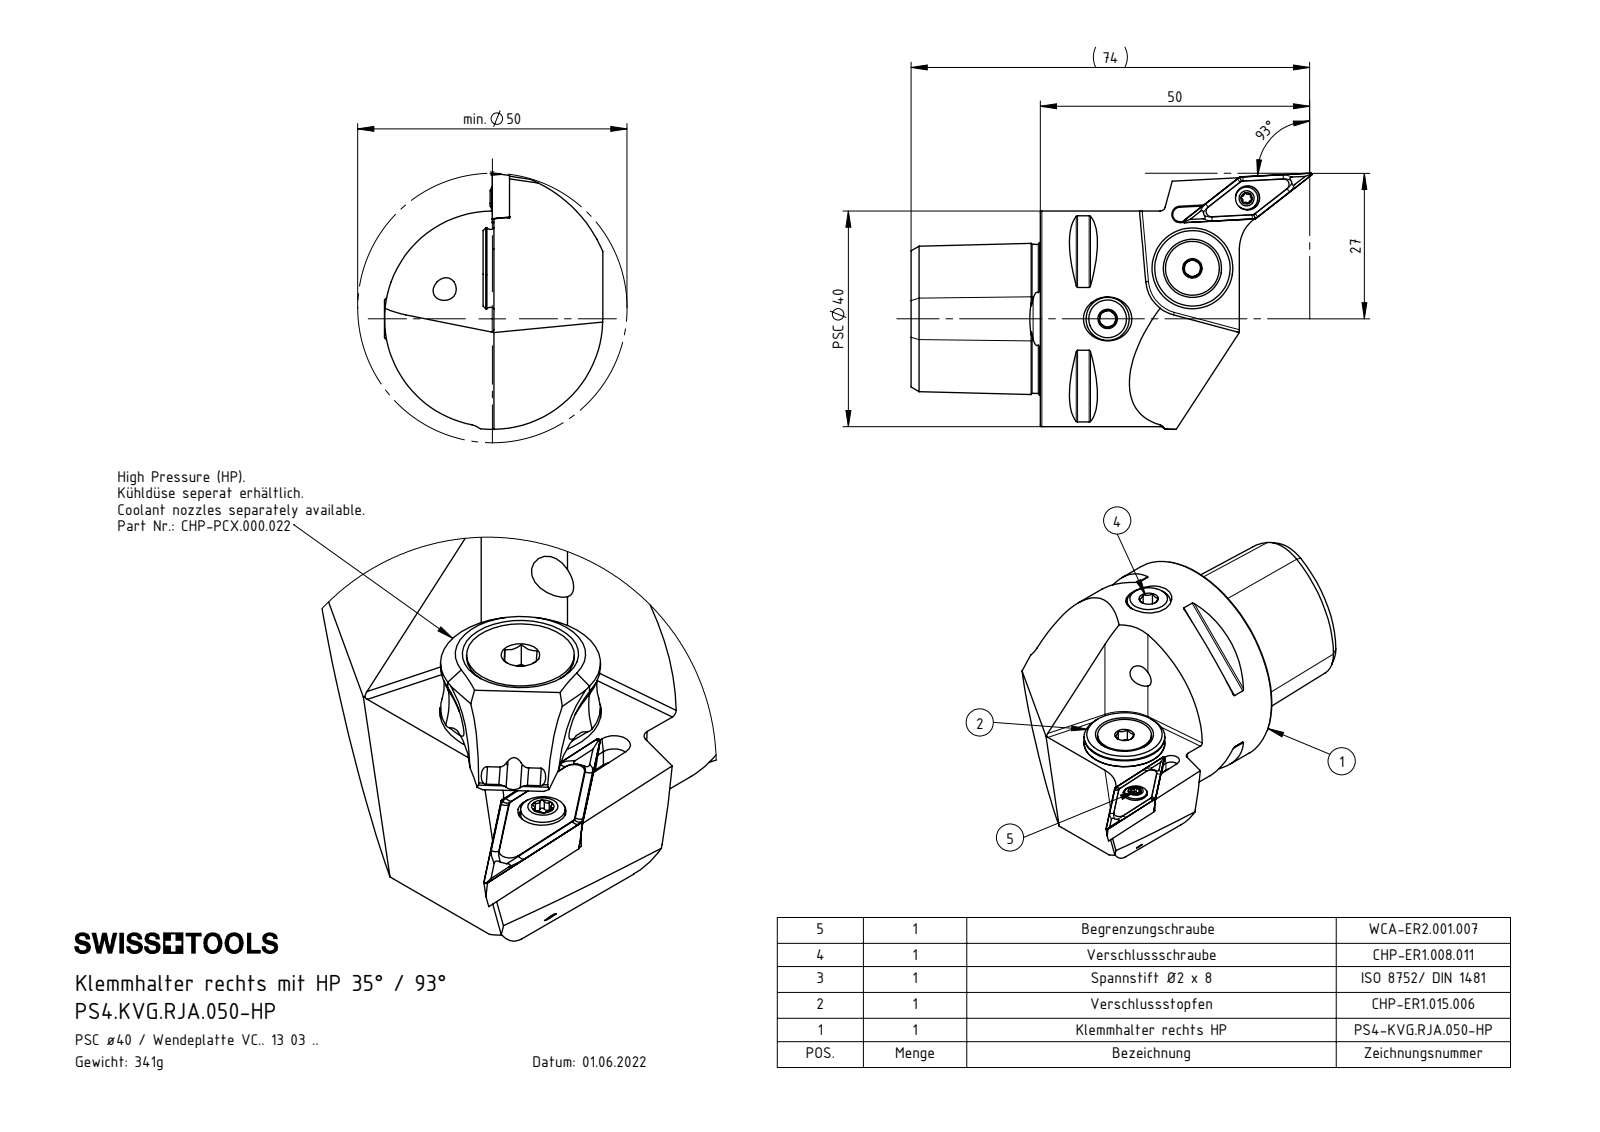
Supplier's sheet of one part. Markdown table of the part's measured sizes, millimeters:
| quantity | value |
| --- | --- |
| part name | CHP-PCX.000.022_Düse; PS4-KVG.RJA.050-HP_B; DIN 7991 - M5x18; CHP-ER1.008.011_A (+7 more) |
| STEP written by | SolidWorks 2022 (AUTOMOTIVE_DESIGN) |
| units | millimeters |
| bodies | 9 solids, 491 faces (107 planar, 134 cylindrical, 250 other) |
| overall size | 74.42 × 47.53 × 40.5 |
| volume | 43 830 mm³ |
| surface area | 15 367 mm² |
| round holes (diameter × count) | 4.2 × 2, 1.2 × 1, 2 × 1, 2.5 × 1, 3 × 1, 3.3 × 1, 3.4 × 1, 4.5 × 1, 4.6 × 1, 5 × 1, 5.3 × 1, 7 × 1 |
| round bosses / shafts (diameter × count) | 40 × 1, 14.85 × 1, 13.4 × 1, 10 × 1, 8 × 1, 5.5 × 1, 5 × 1, 4.15 × 1 |
| partial cylindrical surfaces (radius × count) | 0.3 × 9, 1 × 7, 0.21 × 6, 0.36 × 5, 0.5 × 4, 6 × 3, 1.1 × 2, 1.2 × 2 |
| main face-to-face distances | 2.88, 24, 1.62, 4.5, 15.7, 17.32, 20.2, 15.52, 1.5, 3 |
| hole center spacings | 0.5, 4.49, 12.67, 12.86, 16.42, 16.6, 18.32, 18.75 |
